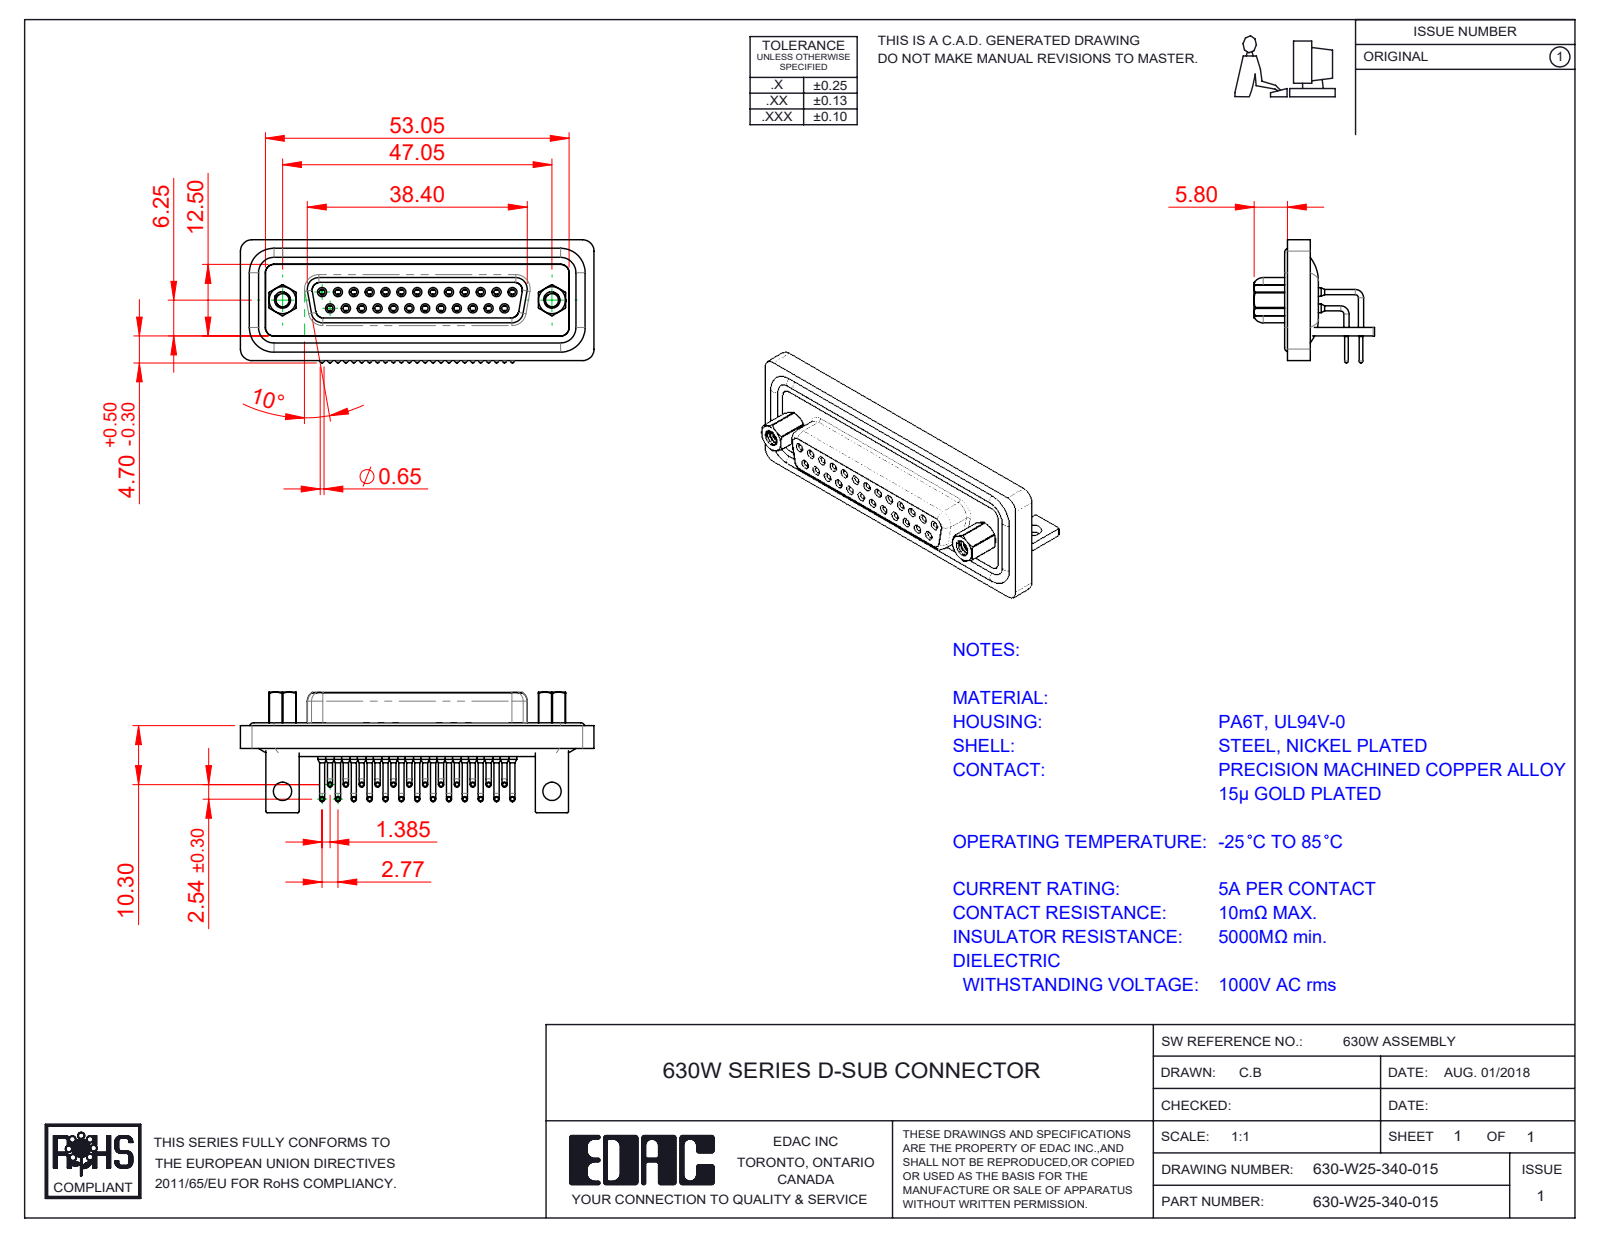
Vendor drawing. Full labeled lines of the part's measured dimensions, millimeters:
Part name (STEP PRODUCT): 630W Waterproof Housing_25 Contacts; 630W 4-40 Hex Standoff; 630W Stabilizer Bracket; 630W Contact Row 2 (+5 more)
STEP written by: SolidWorks 2016 (CONFIG_CONTROL_DESIGN)
Units: millimetres
Bodies: 35 solids, 1844 faces (498 planar, 865 cylindrical, 481 other)
Overall size (bounding box): 61.74 × 21.5 × 21.05
Volume: 7 783 mm³ · Surface area: 14 152 mm²
Round holes (diameter × count): ⌀1 ×25, ⌀1.1 ×25, ⌀1.5 ×25, ⌀1.7 ×25, ⌀1.8 ×25, ⌀2 ×25, ⌀2.26 ×2, ⌀2.29 ×2, ⌀3.2 ×2, ⌀4 ×2, ⌀4.8 ×2, ⌀4.9 ×2
Round bosses / shafts (diameter × count): ⌀0.9 ×50, ⌀1.6 ×29, ⌀0.65 ×25, ⌀2.79 ×2, ⌀5 ×1
Partial cylindrical surfaces — rounded edges, fillets, slot ends (radius × count): R2 ×15, R1.5 ×14, R0.25 ×12, R1.35 ×8, R2.7 ×6, R0.5 ×5, R0.9 ×4, R1.6 ×4
Main face-to-face distances: 0.4, 1.8, 1.6, 9.8, 1.1, 2.9, 2.5, 7.45, 13.65, 1.35
Hole centre spacings: 3.16, 2.77, 5.54, 8.31, 11.08, 13.85, 16.62, 5.03
